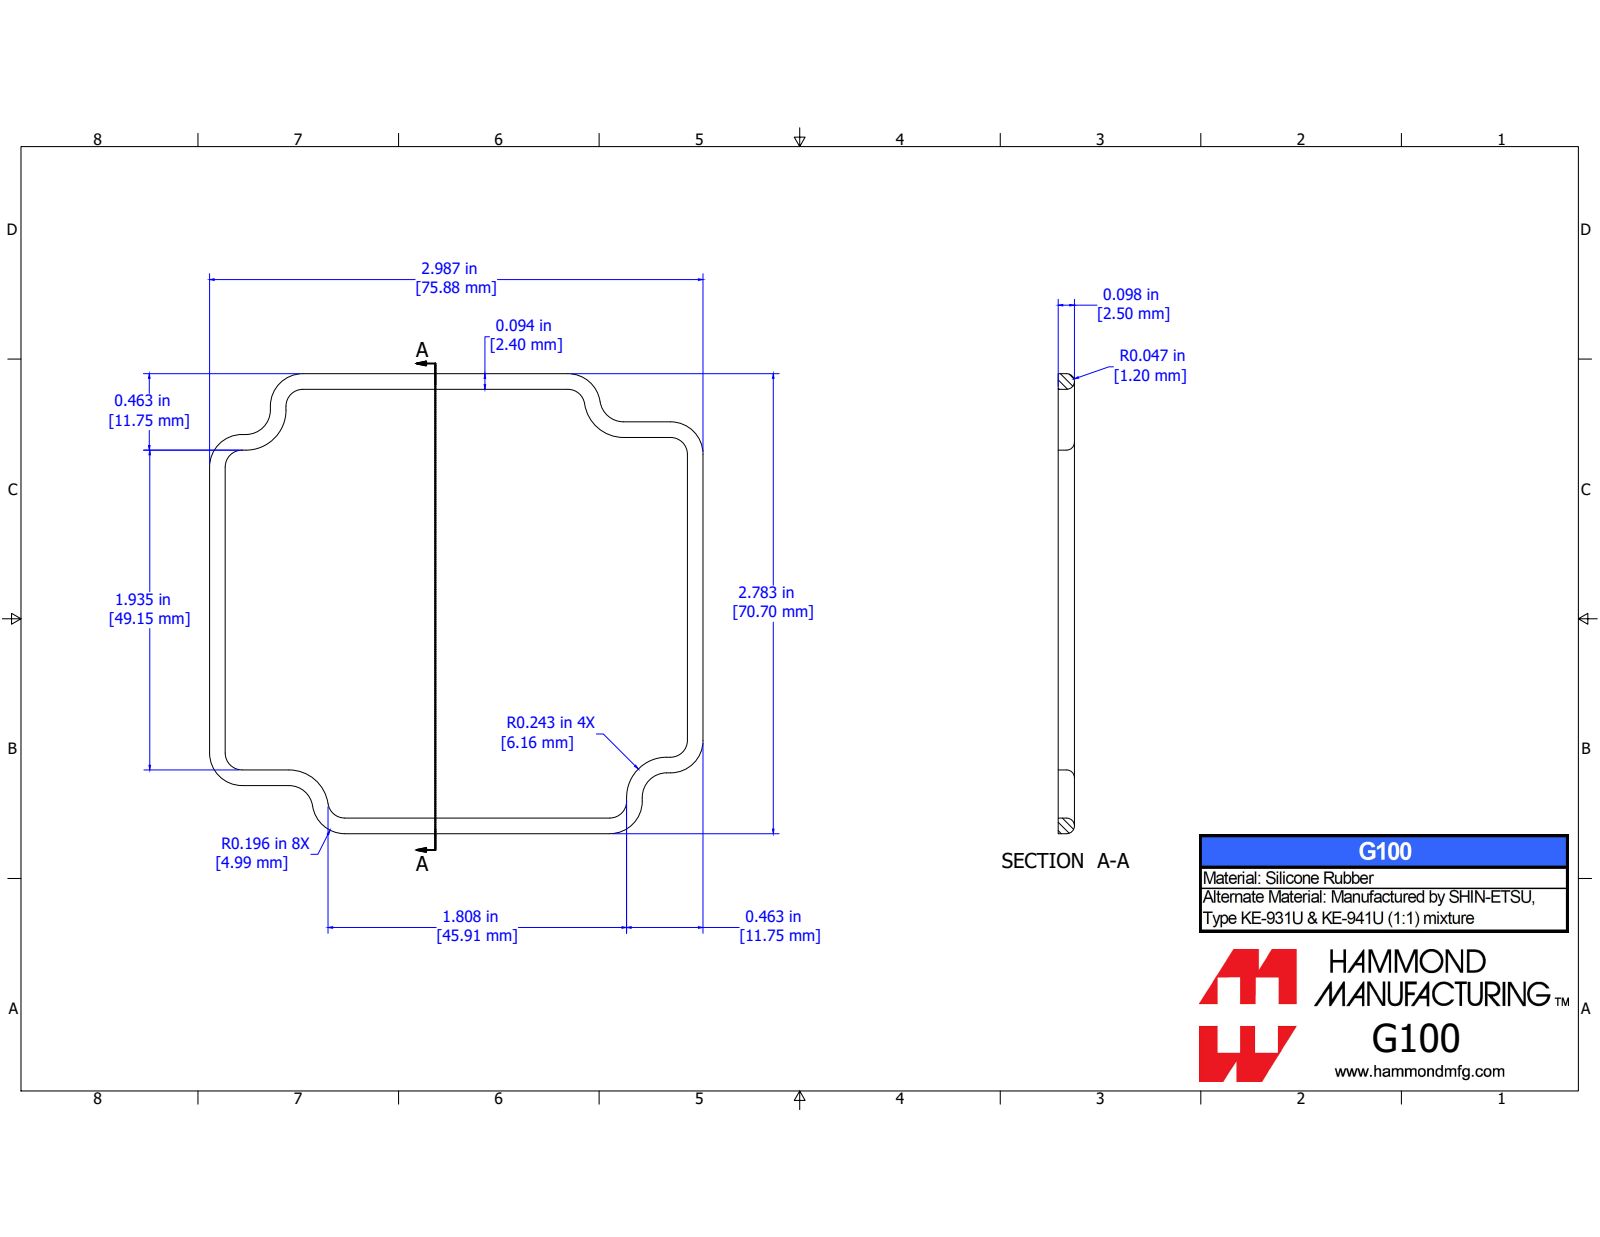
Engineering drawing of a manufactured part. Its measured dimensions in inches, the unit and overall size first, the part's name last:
Units: inches
Overall size (bounding box): 2.978 × 2.782 × 0.108
Partial cylindrical surfaces — rounded edges, fillets, slot ends (radius × count): R0.03 ×12
Main face-to-face distances: 2.894, 2.697, 0.108, 0.323, 2.374, 2.051
Volume: 0.09 in³ · Surface area: 3.74 in²
Bodies: 1 solid, 74 faces (14 planar, 12 cylindrical, 48 other)
Part name (STEP PRODUCT): 1590Z100G
STEP written by: SolidWorks 2019 (CONFIG_CONTROL_DESIGN)
